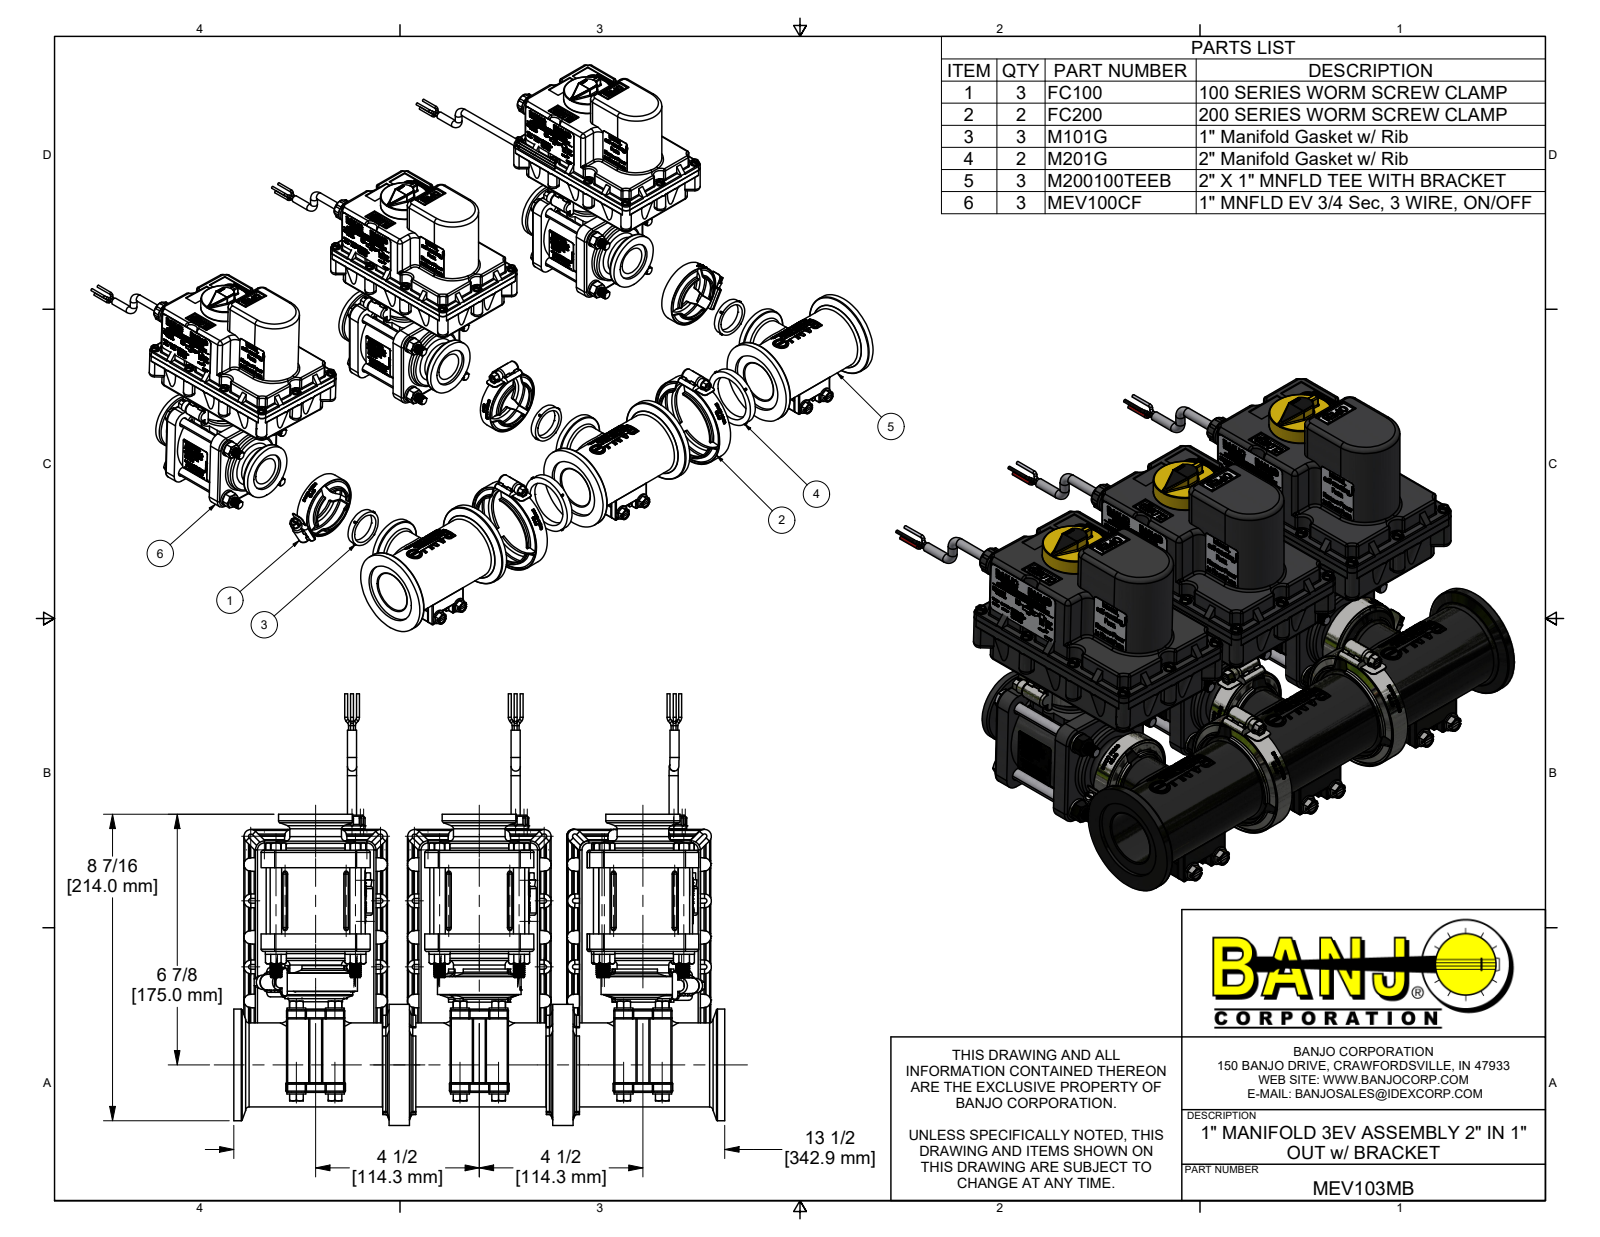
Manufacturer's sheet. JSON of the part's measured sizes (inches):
{"part_name": "MEV103MB; MEV100CF; MEV100XR1; MEV10254A (+8 more)", "step_written_by": "Autodesk Inventor 2022 (AUTOMOTIVE_DESIGN)", "units": "inches", "bodies": {"solids": 244, "faces": 46955, "planar": 23167, "cylindrical": 6194, "other": 17594}, "overall_size": [13.5, 11.866, 8.979], "volume_in3": 217, "surface_area_in2": 2317, "round_holes": [[0.11, 30], [0.16, 30], [0.2, 30], [0.052, 24], [0.079, 24], [0.047, 18], [0.12, 18], [0.15, 18], [0.176, 18], [0.25, 14], [0.252, 12], [0.322, 12]], "round_bosses_or_shafts": [[0.268, 180], [0.328, 30], [0.138, 30], [0.08, 27], [0.103, 24], [0.25, 21], [0.075, 15], [0.583, 12]], "partial_cylinders_radius": [[0.03, 564], [0.02, 211], [0.06, 209], [0.035, 129], [0.125, 110], [0.315, 72], [0.5, 72], [0.062, 60]], "face_to_face_distances": [4.5, 0.125, 0.2, 2.3, 0.125, 1.3, 1.1, 0.075, 0.275, 0.48], "hole_center_spacings": [1.68, 1.775, 4.5, 1.547, 1.785, 2.058, 2.517, 2.837]}
